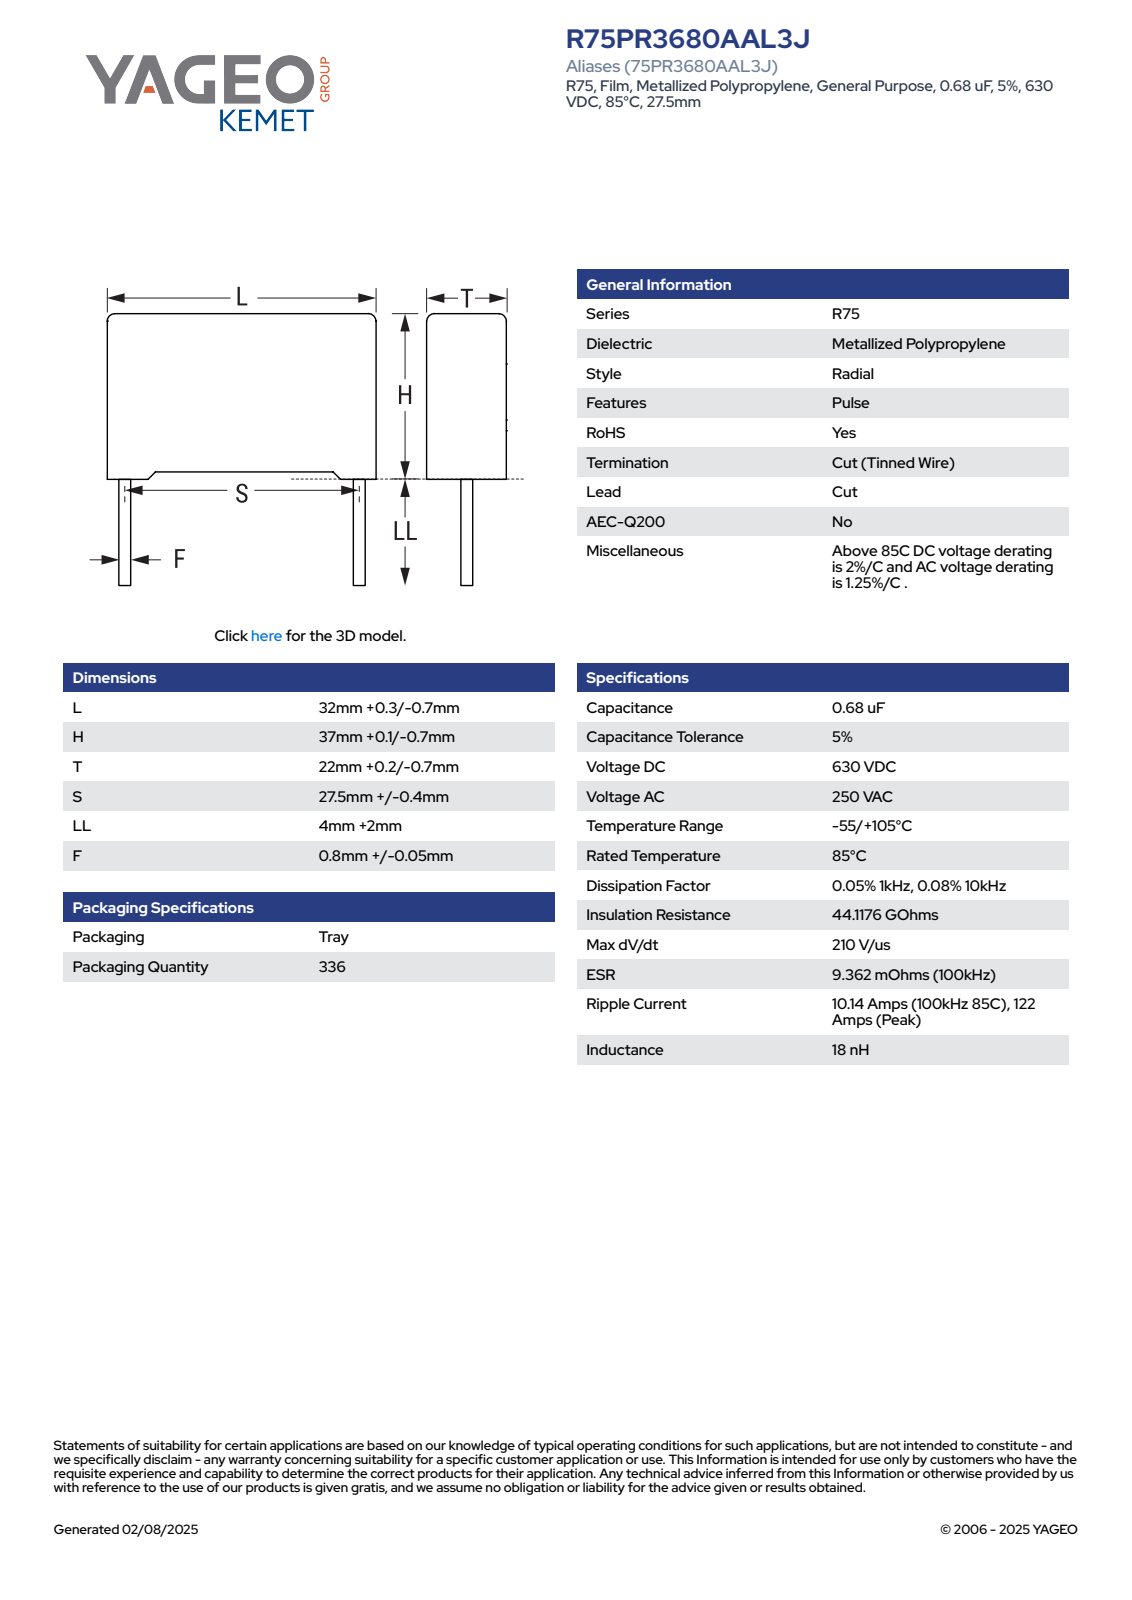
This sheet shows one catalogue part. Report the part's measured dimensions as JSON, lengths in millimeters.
{"part_name": "CFR_RB2_32X37X22_L32.3H15.1T24.2S27.5LL6F0.85", "step_written_by": "SolidWorks 2021 (AUTOMOTIVE_DESIGN)", "units": "millimeters", "bodies": {"solids": 4, "faces": 85, "planar": 77, "cylindrical": 8, "other": 0}, "overall_size": [32.3, 24.2, 21.1], "volume_mm3": 11280, "surface_area_mm2": 3389, "round_bosses_or_shafts": [[0.85, 2]], "partial_cylinders_radius": [[0.5, 4]], "face_to_face_distances": [14.35, 24.2, 32.3, 0.75, 15.1, 1.08, 0.52, 14.58, 31.22, 23.12]}
